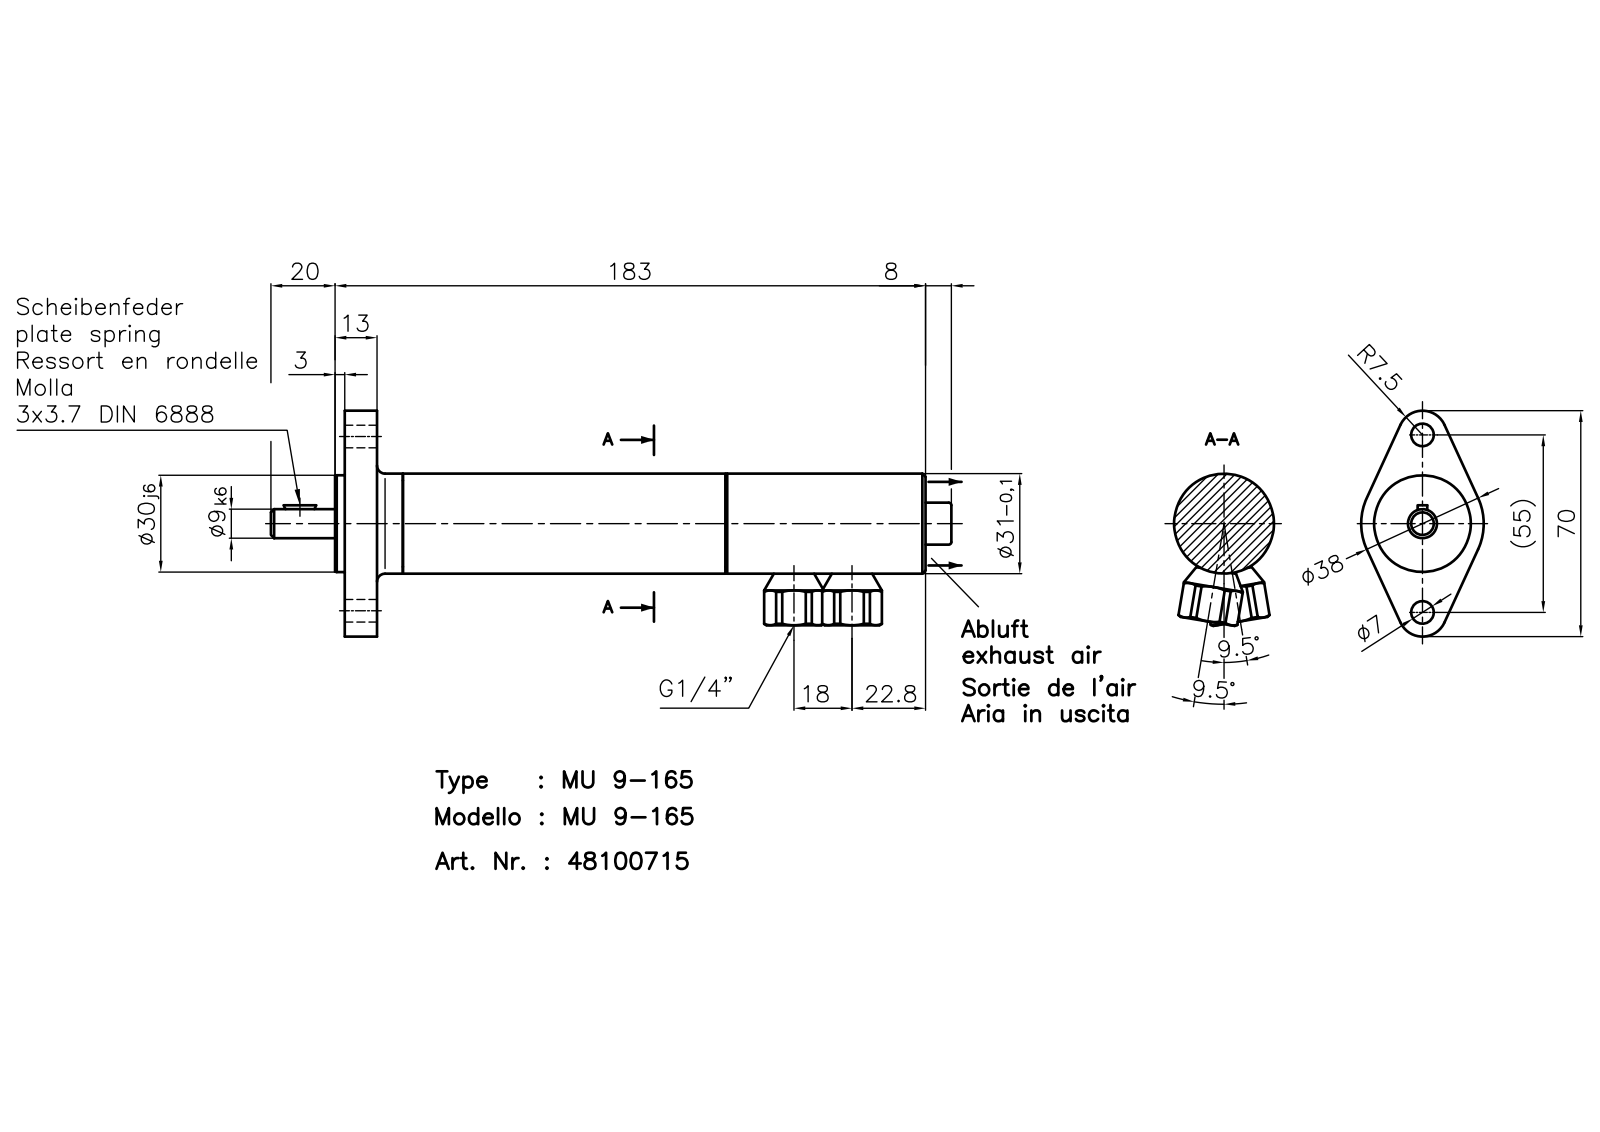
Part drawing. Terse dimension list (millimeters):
name: MU 9-165_48100715
written by: Autodesk Inventor 2008 (AUTOMOTIVE_DESIGN)
unit: mm
bodies: 1 solid, 150 faces (69 planar, 49 cylindrical, 32 other)
size: 211.1 × 70 × 38.8
volume: 153 114 mm³; area: 31 487 mm²
holes: 1× ⌀2.8, 1× ⌀10
bosses: 1× ⌀31, 1× ⌀30, 1× ⌀28, 1× ⌀26.79, 1× ⌀13, 1× ⌀9, 1× ⌀8
rounds: 8× R4, 4× R8, 2× R7, 2× R7.5, 1× R5, 1× R5.25, 1× R12.66, 1× R12.75
face distances: 10, 3, 170.1, 13, 183.1, 180.1, 37.98, 17.01, 1.05, 99.05
